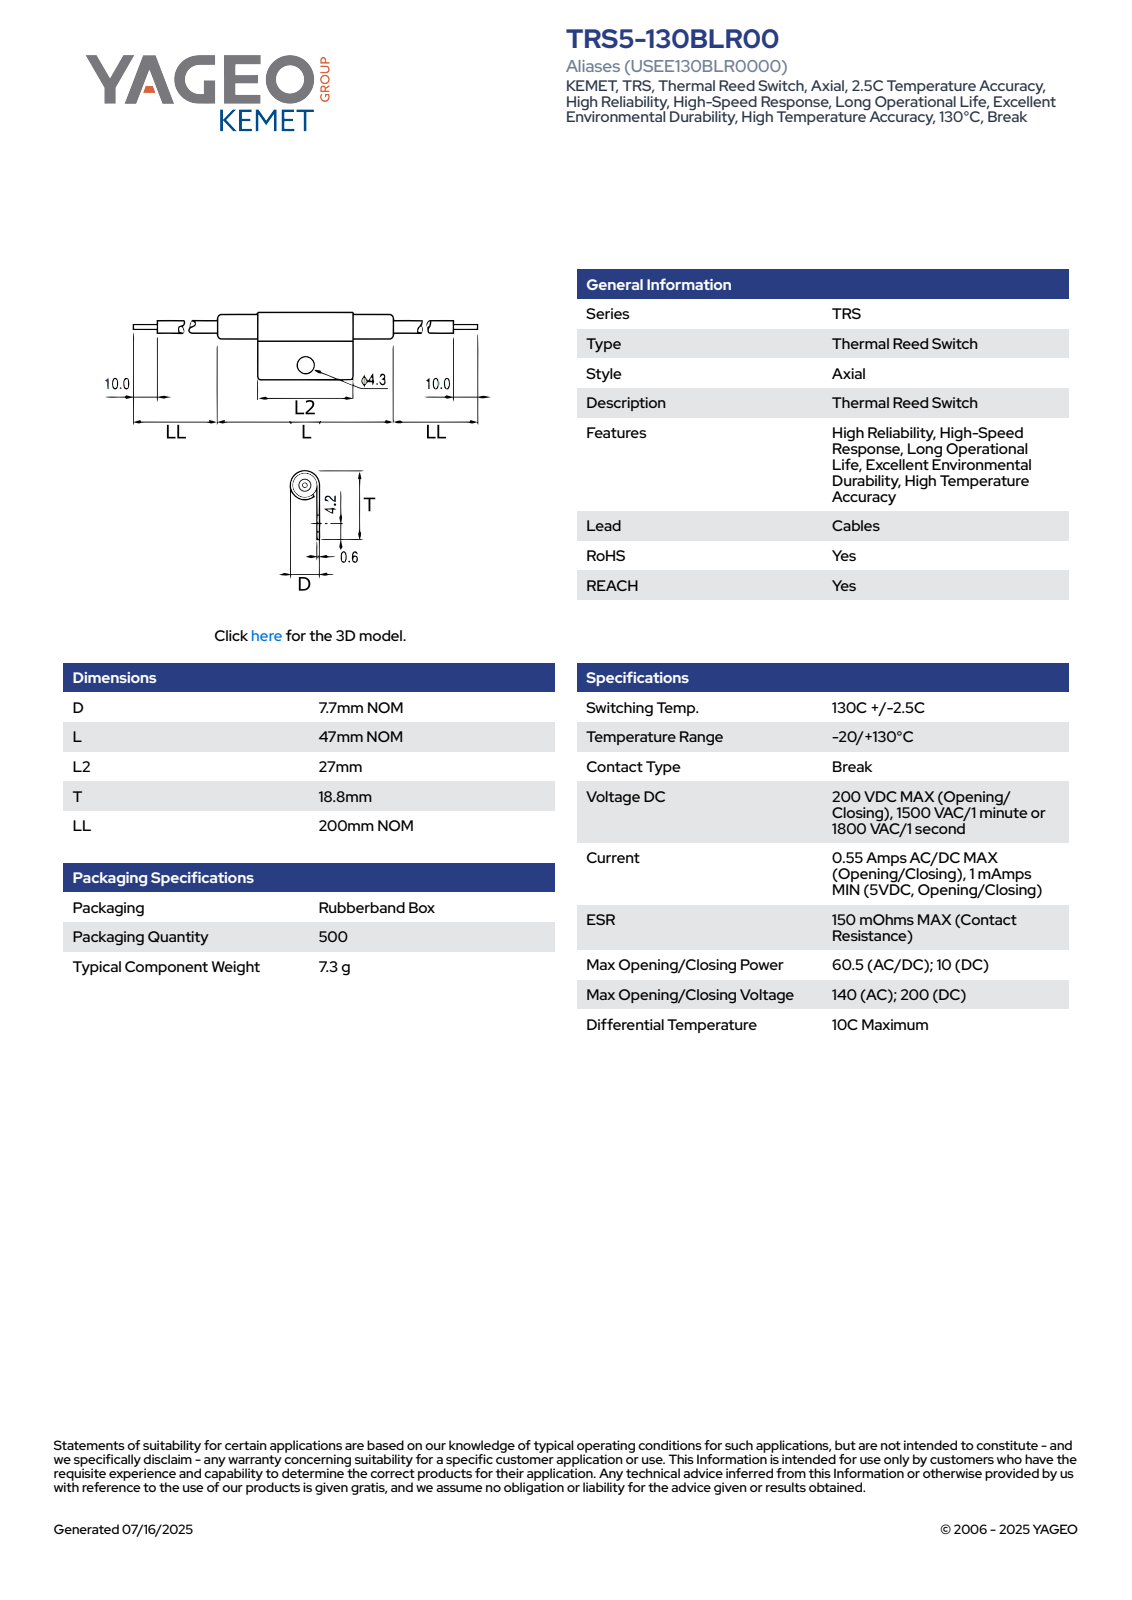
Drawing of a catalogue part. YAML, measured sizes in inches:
part_name: "ST_TRSL_D7.7L47L227T18.8LL200"
step_written_by: "SolidWorks 2014 (AUTOMOTIVE_DESIGN)"
units: inches
bodies: {solids: 1, faces: 90, planar: 33, cylindrical: 22, other: 35}
overall_size: [17.598, 0.74, 0.303]
volume: 0.161
surface_area: 4.834
round_holes:
  - {diameter: 0.169, count: 1}
round_bosses_or_shafts:
  - {diameter: 0.303, count: 1}
  - {diameter: 0.293, count: 1}
  - {diameter: 0.039, count: 1}
  - {diameter: 0.02, count: 1}
partial_cylinders:
  - {radius: 0.079, count: 2}
  - {radius: 0.151, count: 1}
face_to_face_distances: [0.024, 1.85, 0.394, 1.457, 1.063, 7.874, 9.331, 7.48, 8.937, 16.811]
